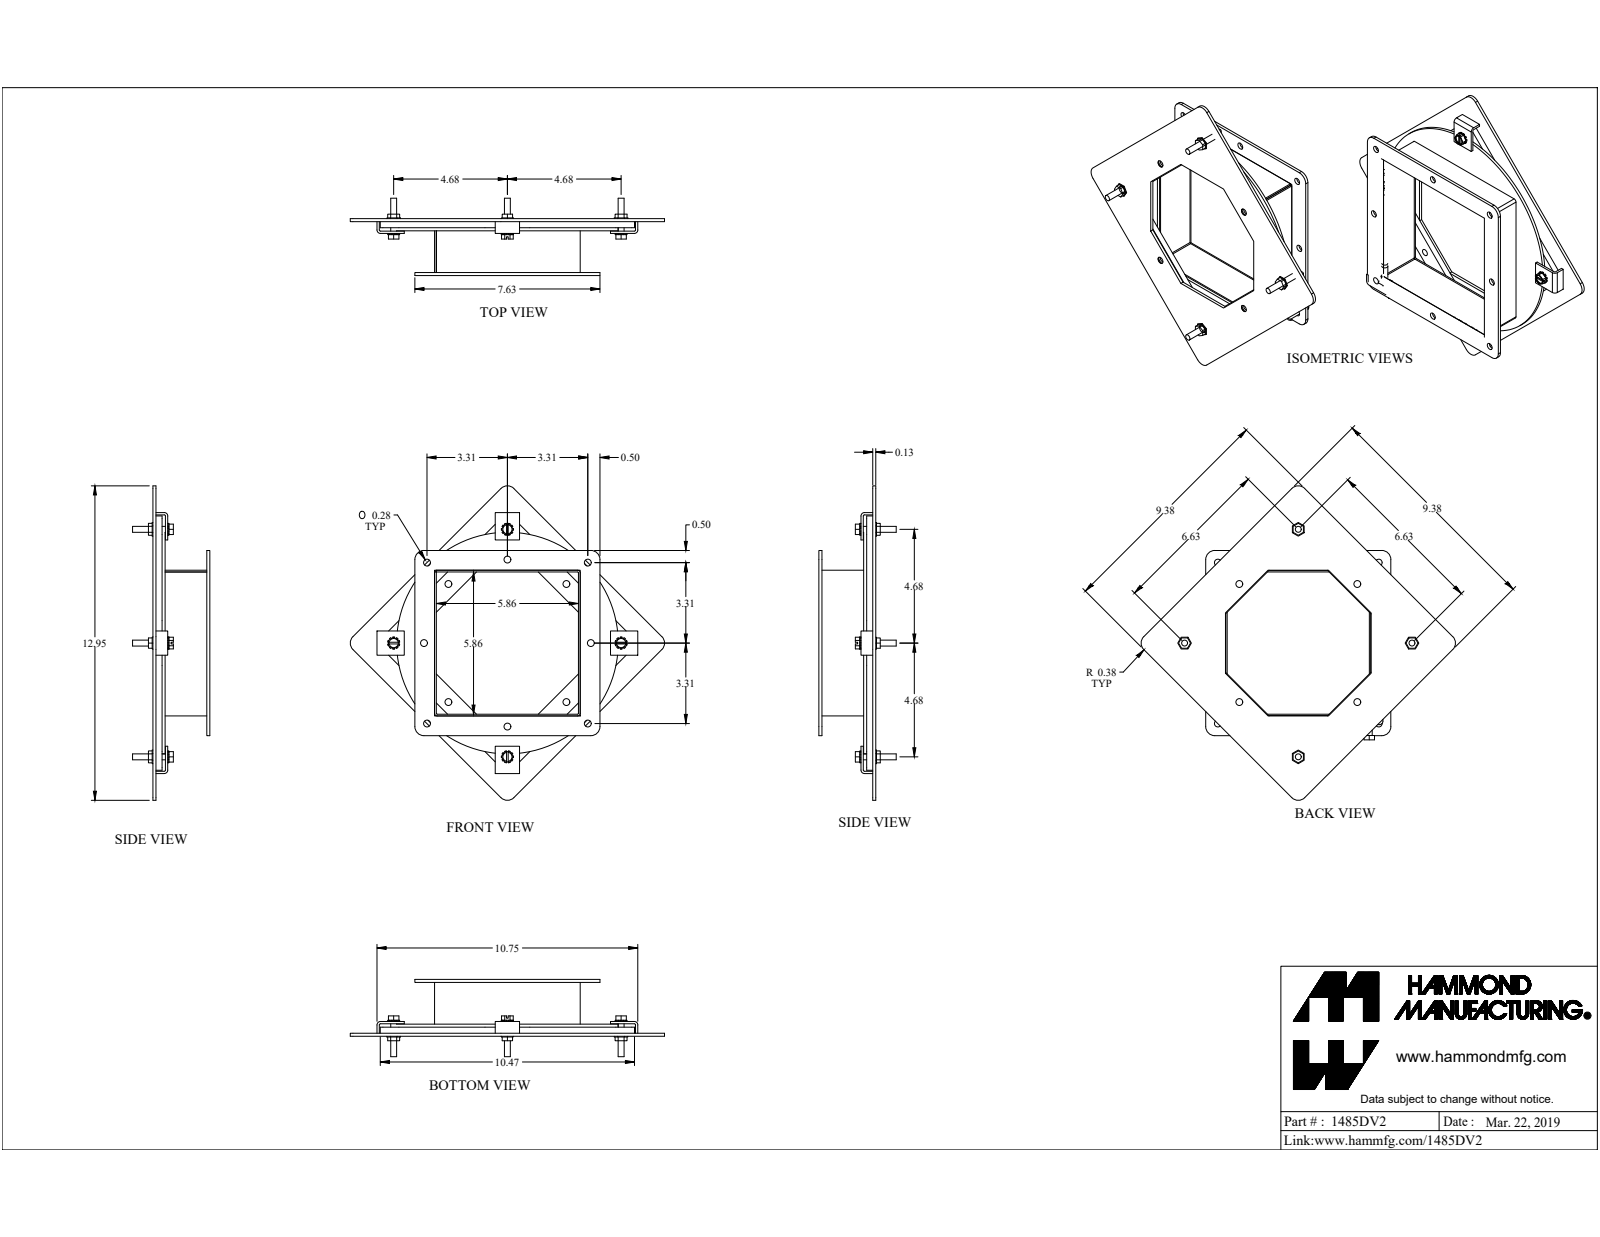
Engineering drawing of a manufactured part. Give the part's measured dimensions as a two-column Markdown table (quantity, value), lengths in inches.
| quantity | value |
| --- | --- |
| part name | 1485DV2 |
| STEP written by | SolidWorks 2019 (CONFIG_CONTROL_DESIGN) |
| units | inches |
| bodies | 40 solids, 759 faces (532 planar, 202 cylindrical, 25 other) |
| overall size | 12.948 × 12.948 × 3.434 |
| volume | 41.5 in³ |
| surface area | 627 in² |
| round holes (diameter × count) | 0.281 × 16, 0.375 × 6, 0.196 × 5, 0.258 × 5, 0.312 × 4, 0.187 × 2, 0.265 × 2, 0.313 × 2, 0.224 × 1, 0.35 × 1 |
| round bosses / shafts (diameter × count) | 0.244 × 5, 0.25 × 3, 0.563 × 2, 9.125 × 1, 0.52 × 1, 0.455 × 1, 0.246 × 1 |
| partial cylindrical surfaces (radius × count) | 0.25 × 13, 0.375 × 12, 0.048 × 9, 0.143 × 9, 0.062 × 4, 0.036 × 3, 0.108 × 3, 0.06 × 1 |
| main face-to-face distances | 0.25, 0.375, 0.125, 2.218, 0.125, 1.843, 0.375, 2.593, 2.093, 1.968 |
| hole center spacings | 3.315, 7.519, 4.861, 5.81, 5.811, 6.615, 6.625, 2.631 |
